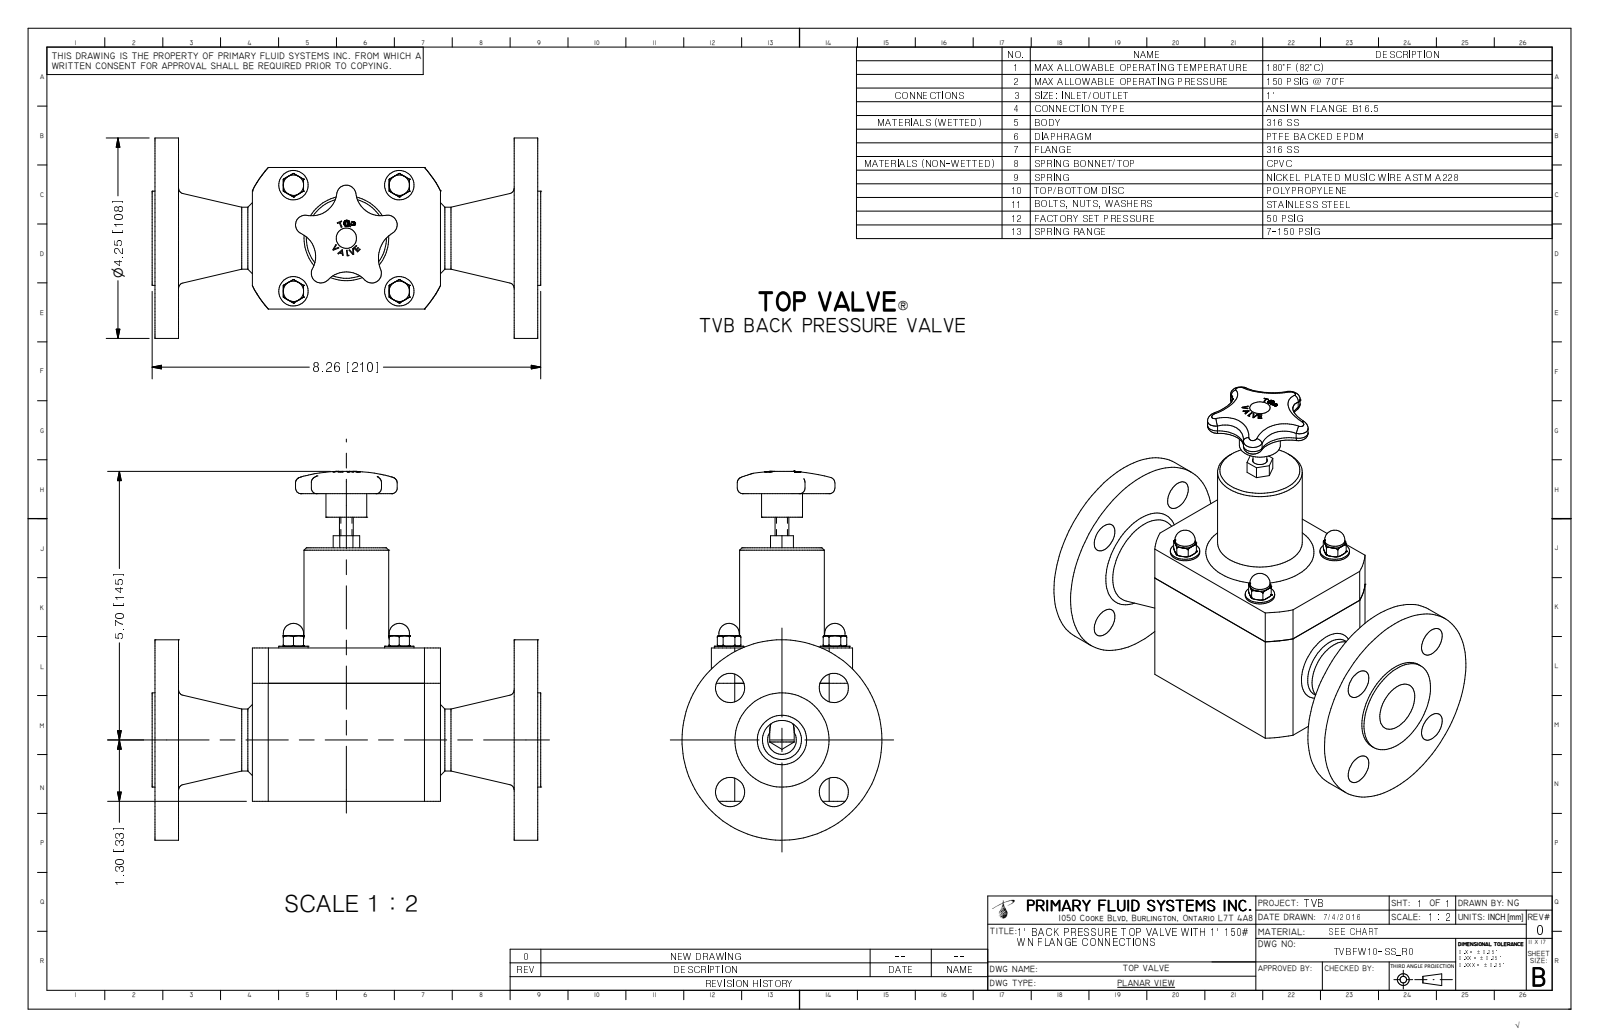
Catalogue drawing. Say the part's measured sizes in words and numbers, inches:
The part is named "TVBFW10-SS-R0". Its 3-D file was written by "Autodesk Inventor 2009 (AUTOMOTIVE_DESIGN)". It is 1 solid with 369 faces: 154 planar, 63 cylindrical and 152 other. Overall it measures 8.26 by 7.822 by 4.25 inches. Its volume is 60.88 cubic inches and its surface area 188.1 square inches. Round holes: 4 of diameter 0.175, 4 of diameter 0.62, 1 of diameter 1.049. Round bosses or shafts: 4 of diameter 0.625, 4 of diameter 0.433, 4 of diameter 0.375, 1 of diameter 4.25, 1 of diameter 2, 1 of diameter 1.8, 1 of diameter 1.315, 1 of diameter 0.87. Partial cylindrical surfaces (rounded edges, fillets, slot ends): 5 of radius 0.085, 5 of radius 0.205, 4 of radius 0.536, 4 of radius 0.656, 1 of radius 0.625, 1 of radius 0.745, 1 of radius 2.238, 1 of radius 2.238. The main face-to-face distances are 0.5, 7.635, 3, 8.135, 2.067, 6.067, 1.567, 5.567, 7.135, 3.25. The hole center spacings are 1.56, 2.206, 2.25, 3.12, 3.182.
